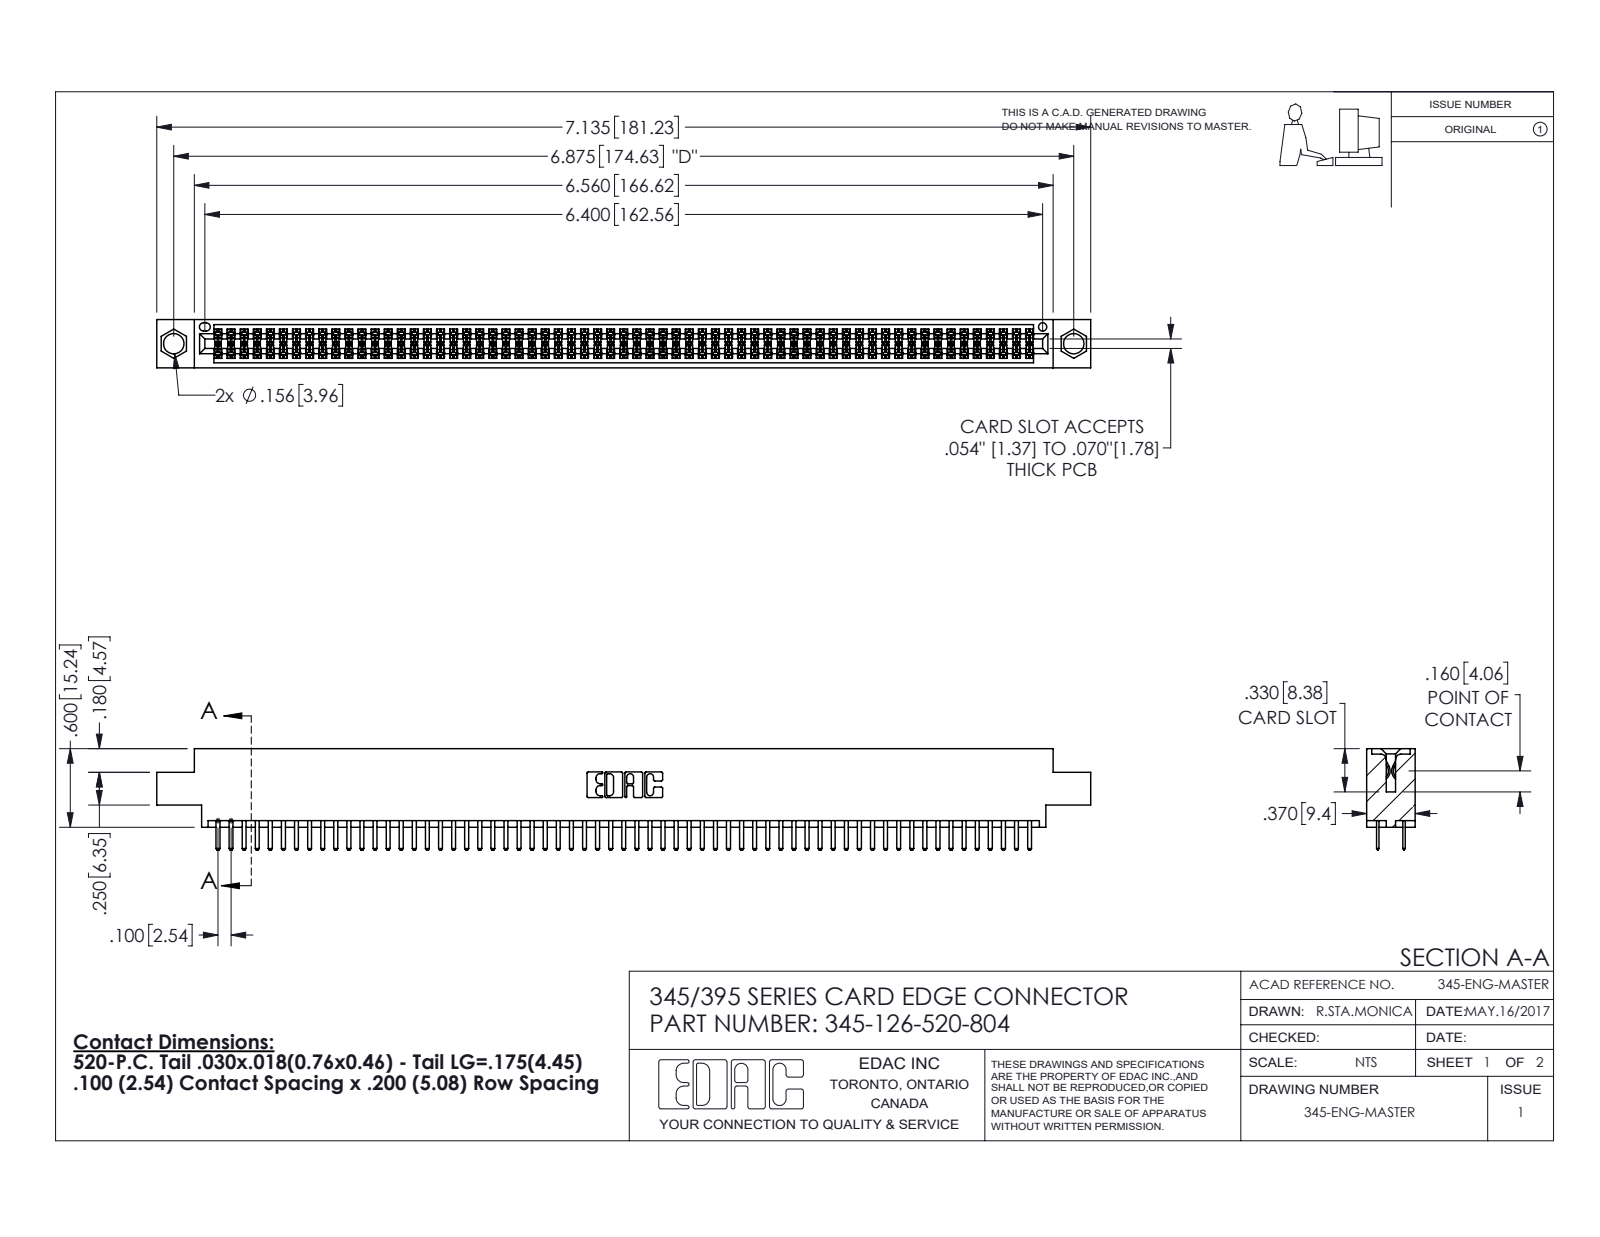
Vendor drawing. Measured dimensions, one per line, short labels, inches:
name: 345 Part_0.170 Offset - 0.156 Dia-TI; 345-126-520-804; 345-292-001_345-293-120
written by: SolidWorks 2020 (CONFIG_CONTROL_DESIGN)
unit: in
bodies: 127 solids, 6948 faces (4508 planar, 2440 cylindrical, 0 other)
size: 7.135 × 0.775 × 0.37
volume: 1.069 in³; area: 40.59 in²
holes: 2× ⌀0.156, 1× ⌀0.064
rounds: 189× R0.006, 130× R0.01, 22× R0.01, 6× R0.007, 6× R0.031, 3× R0.026, 2× R0.014, 2× R0.019
face distances: 0.072, 0.298, 0.2, 0.37, 0.098, 0.272, 0.025, 0.225, 0.022, 0.072
hole spacings: 0.27, 6.639, 6.875
